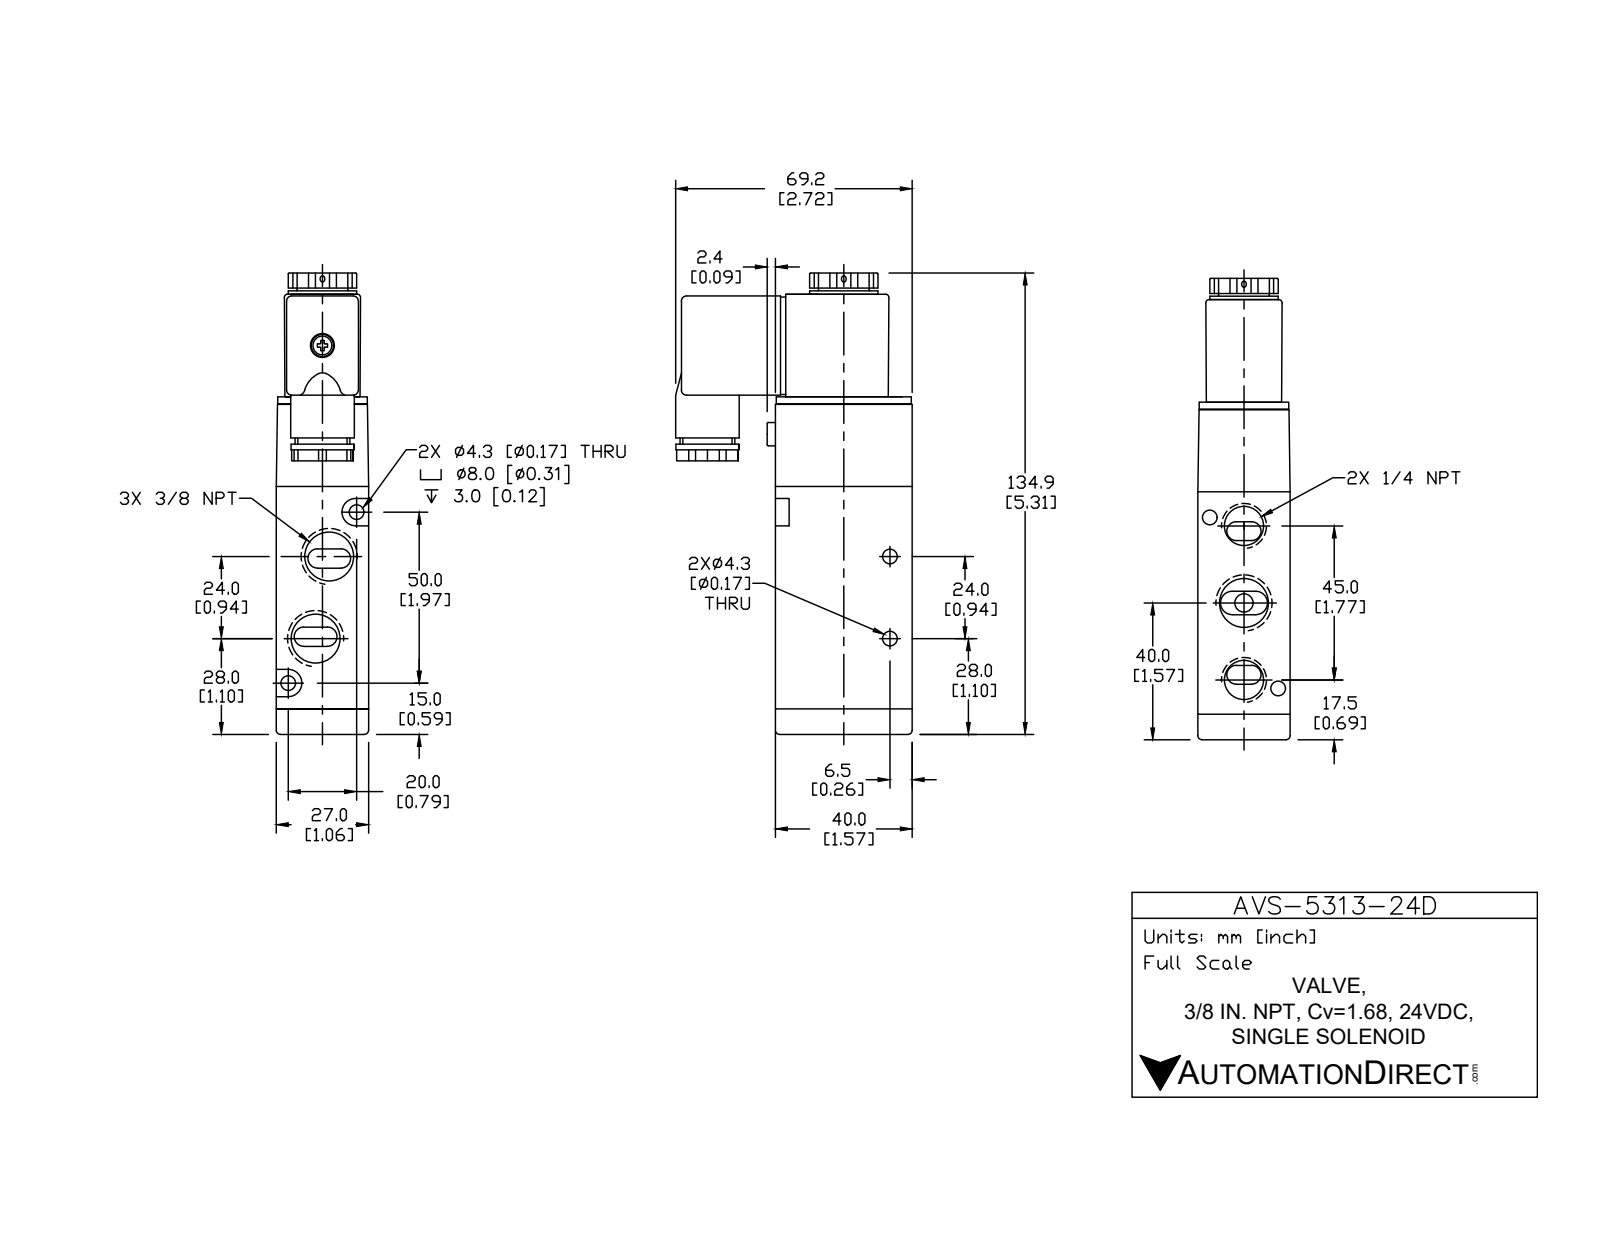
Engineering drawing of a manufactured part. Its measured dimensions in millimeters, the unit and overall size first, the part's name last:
Units: millimetres
Overall size (bounding box): 134.9 × 69.2 × 27
Round holes (diameter × count): ⌀4.3 ×4, ⌀14.27 ×3, ⌀11.13 ×2, ⌀9.3 ×1
Round bosses / shafts (diameter × count): ⌀20 ×1, ⌀18.6 ×1, ⌀18.4 ×1, ⌀16 ×1, ⌀14.8 ×1, ⌀6.7 ×1
Partial cylindrical surfaces — rounded edges, fillets, slot ends (radius × count): R1.5 ×12, R3 ×12, R0.5 ×8, R1 ×5
Main face-to-face distances: 27, 65, 40, 24, 3, 7.5, 72.5, 29.5, 21, 27.5
Hole centre spacings: 10.31, 10.69, 12.17, 15.26, 22.5, 26.93, 34.56, 38.9
Volume: 137 713 mm³ · Surface area: 32 379 mm²
Bodies: 4 solids, 192 faces (88 planar, 77 cylindrical, 27 other)
Part name (STEP PRODUCT): AVS-5313-24D
STEP written by: SolidWorks 2015 (CONFIG_CONTROL_DESIGN)
